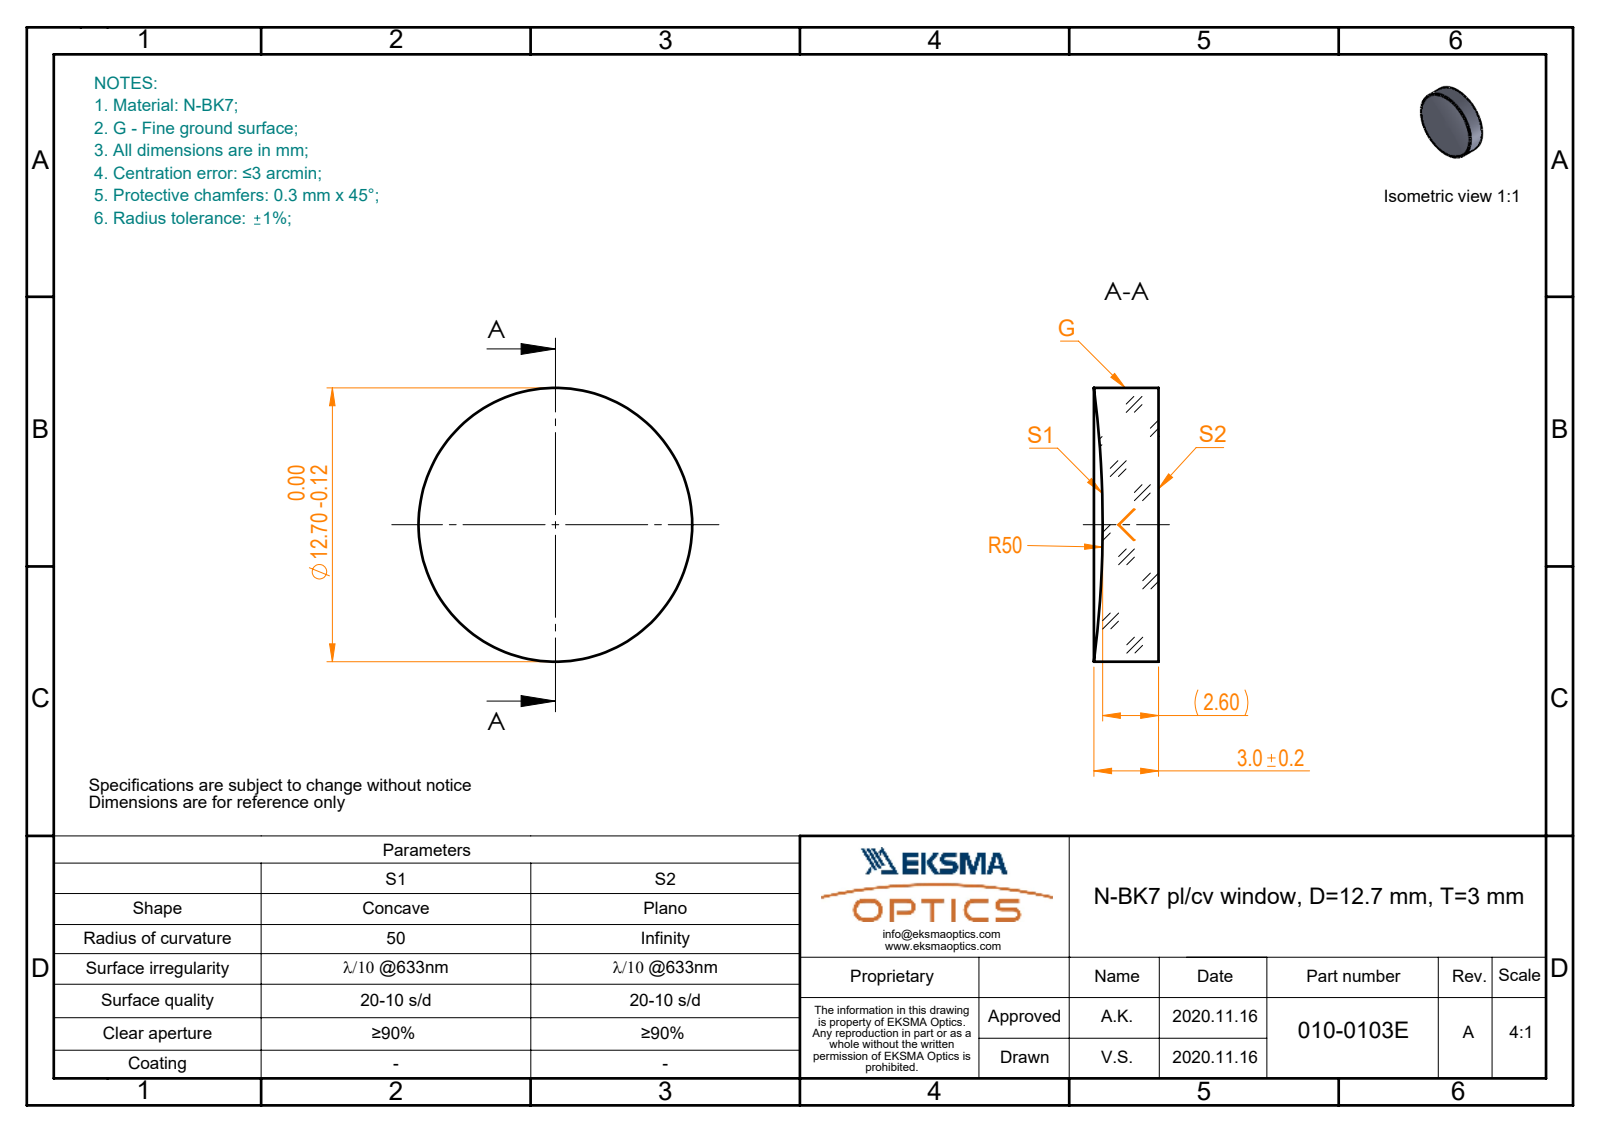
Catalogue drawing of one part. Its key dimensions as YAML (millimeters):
part_name: "010-0103E_N-BK7_PCV_window"
step_written_by: "SolidWorks 2019 (CONFIG_CONTROL_DESIGN)"
units: millimeters
bodies: {solids: 1, faces: 5, planar: 1, cylindrical: 2, other: 2}
overall_size: [12.7, 12.7, 3]
volume: 354
surface_area: 374
round_bosses_or_shafts:
  - {diameter: 12.7, count: 1}
